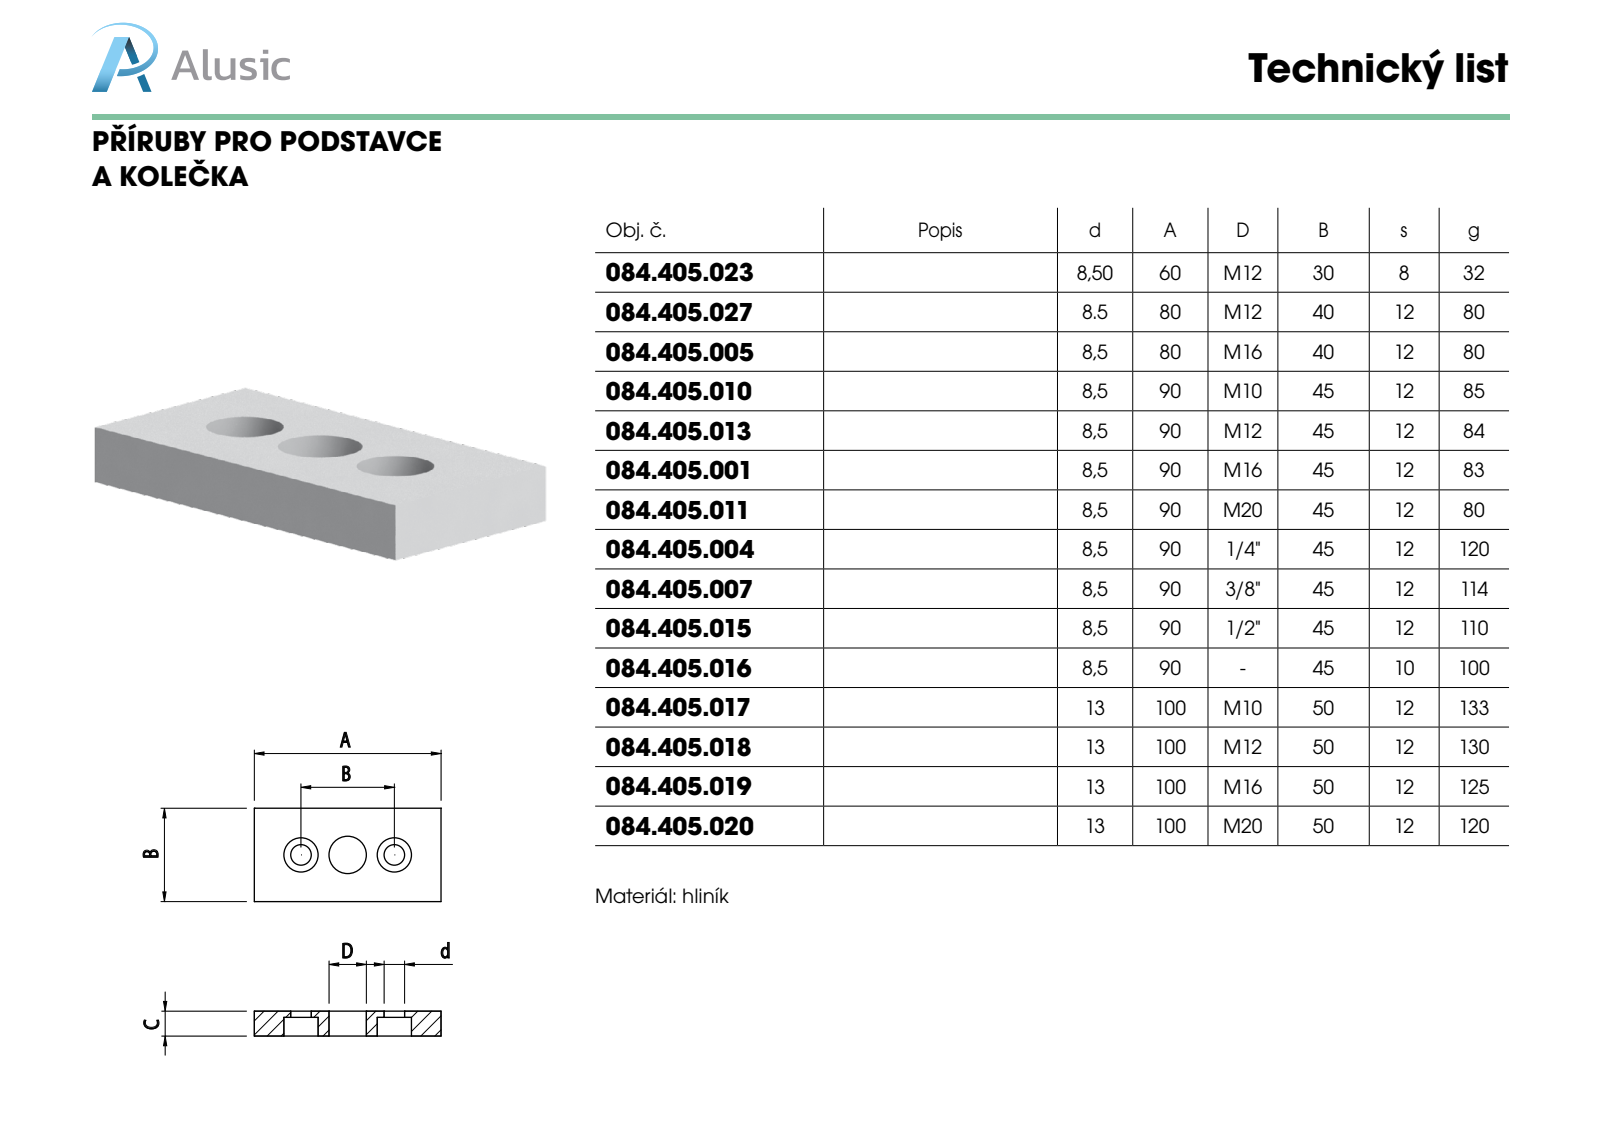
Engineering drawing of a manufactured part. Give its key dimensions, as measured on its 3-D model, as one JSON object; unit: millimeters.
{"part_name": "084.405.020", "step_written_by": "SolidWorks 2012 (AUTOMOTIVE_DESIGN)", "units": "millimeters", "bodies": {"solids": 1, "faces": 17, "planar": 8, "cylindrical": 9, "other": 0}, "overall_size": [100, 50, 12], "volume_mm3": 52010, "surface_area_mm2": 14375, "round_holes": [[13, 2], [19.5, 2], [17.5, 1]], "partial_cylinders_radius": [[3, 4]], "face_to_face_distances": [12, 50, 100, 6.5, 5.5], "hole_center_spacings": [25, 50]}
